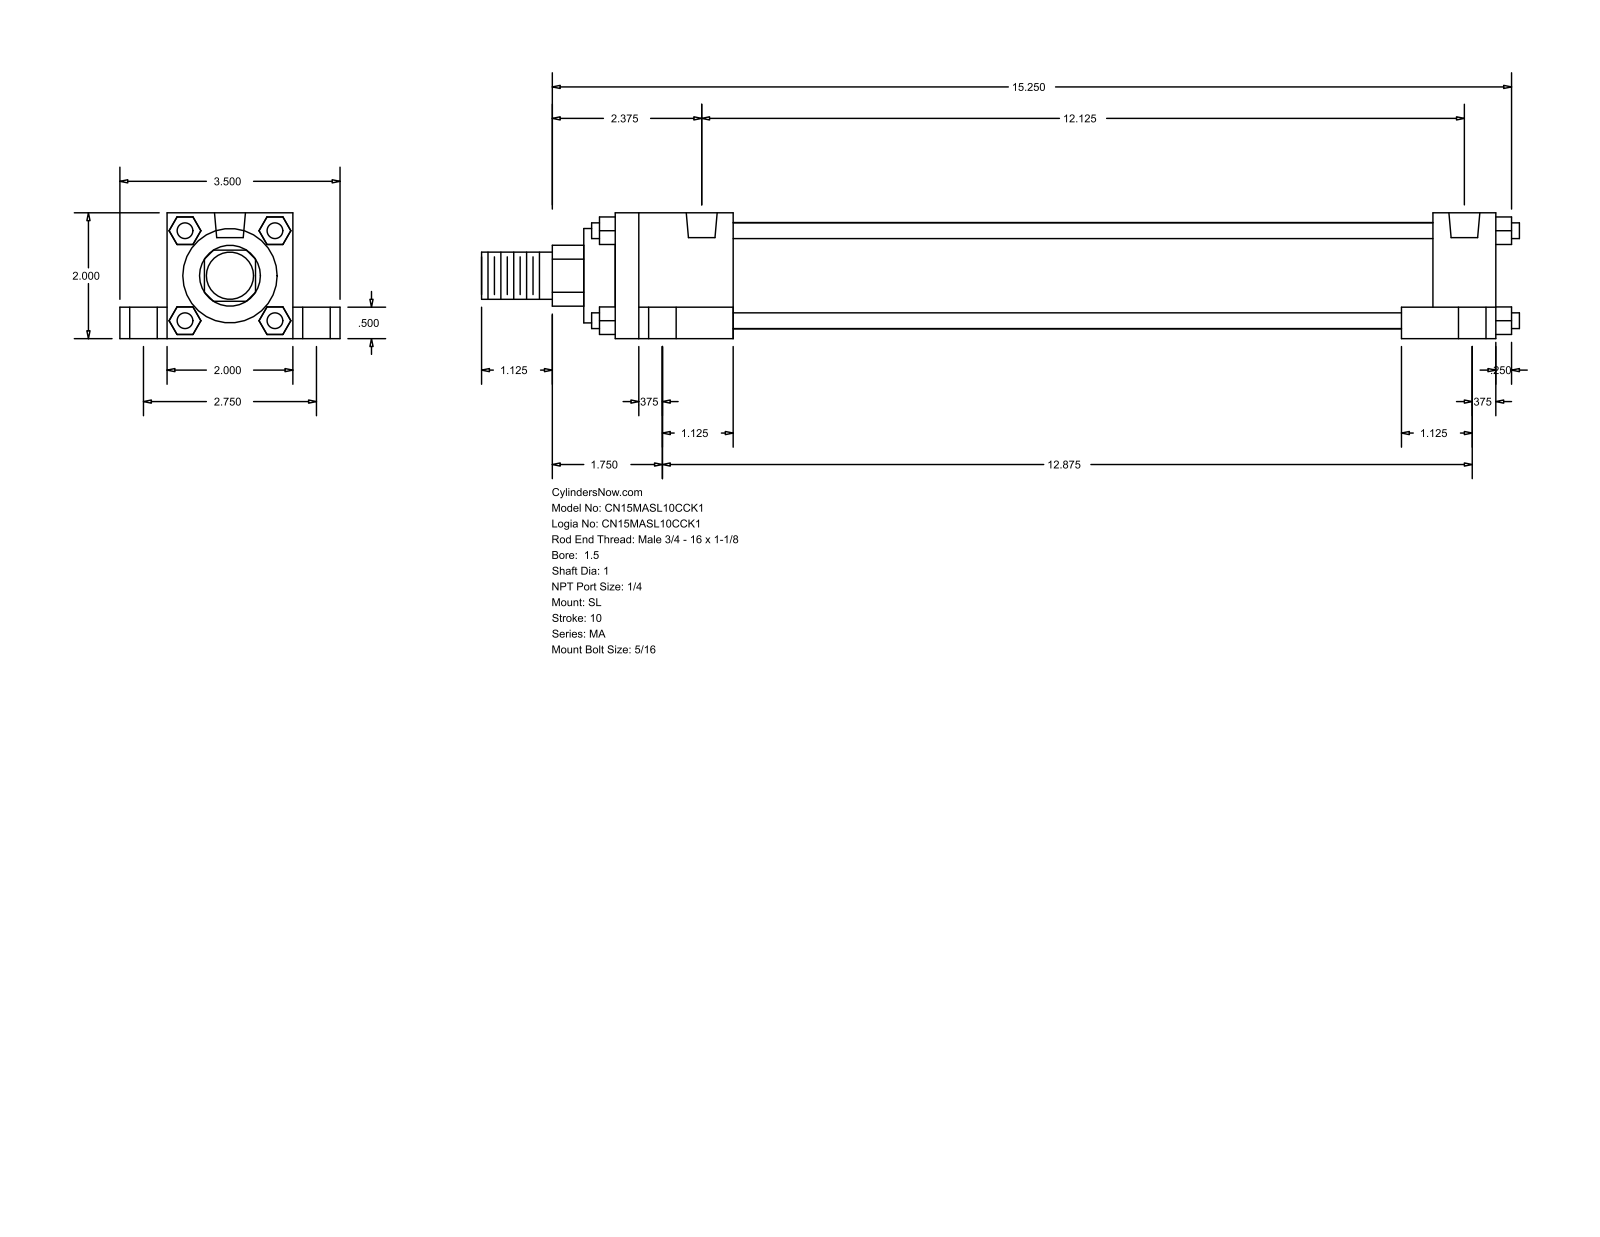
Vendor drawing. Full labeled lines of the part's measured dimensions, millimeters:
Part name (STEP PRODUCT): MA_SL__0150_1
STEP written by: GSSL Pune (CONFIG_CONTROL_DESIGN)
Units: millimetres
Bodies: 0 solids, 148 faces (112 planar, 36 cylindrical, 0 other)
Overall size (bounding box): 419.1 × 88.9 × 50.8
Round holes (diameter × count): ⌀7.94 ×4, ⌀11.11 ×4, ⌀17.46 ×4, ⌀12.49 ×2
Round bosses / shafts (diameter × count): ⌀6.35 ×4, ⌀42.93 ×1, ⌀38.1 ×1, ⌀25.4 ×1, ⌀19.05 ×1
Partial cylindrical surfaces — rounded edges, fillets, slot ends (radius × count): R12.29 ×1
Main face-to-face distances: 50.8, 12.7, 19.05, 69.85, 38.1, 9.52, 355.6, 25.4, 6.35, 330.2
Hole centre spacings: 35.06, 38.36, 69.84, 307.97, 313.1, 325.73, 327.03, 334.4
